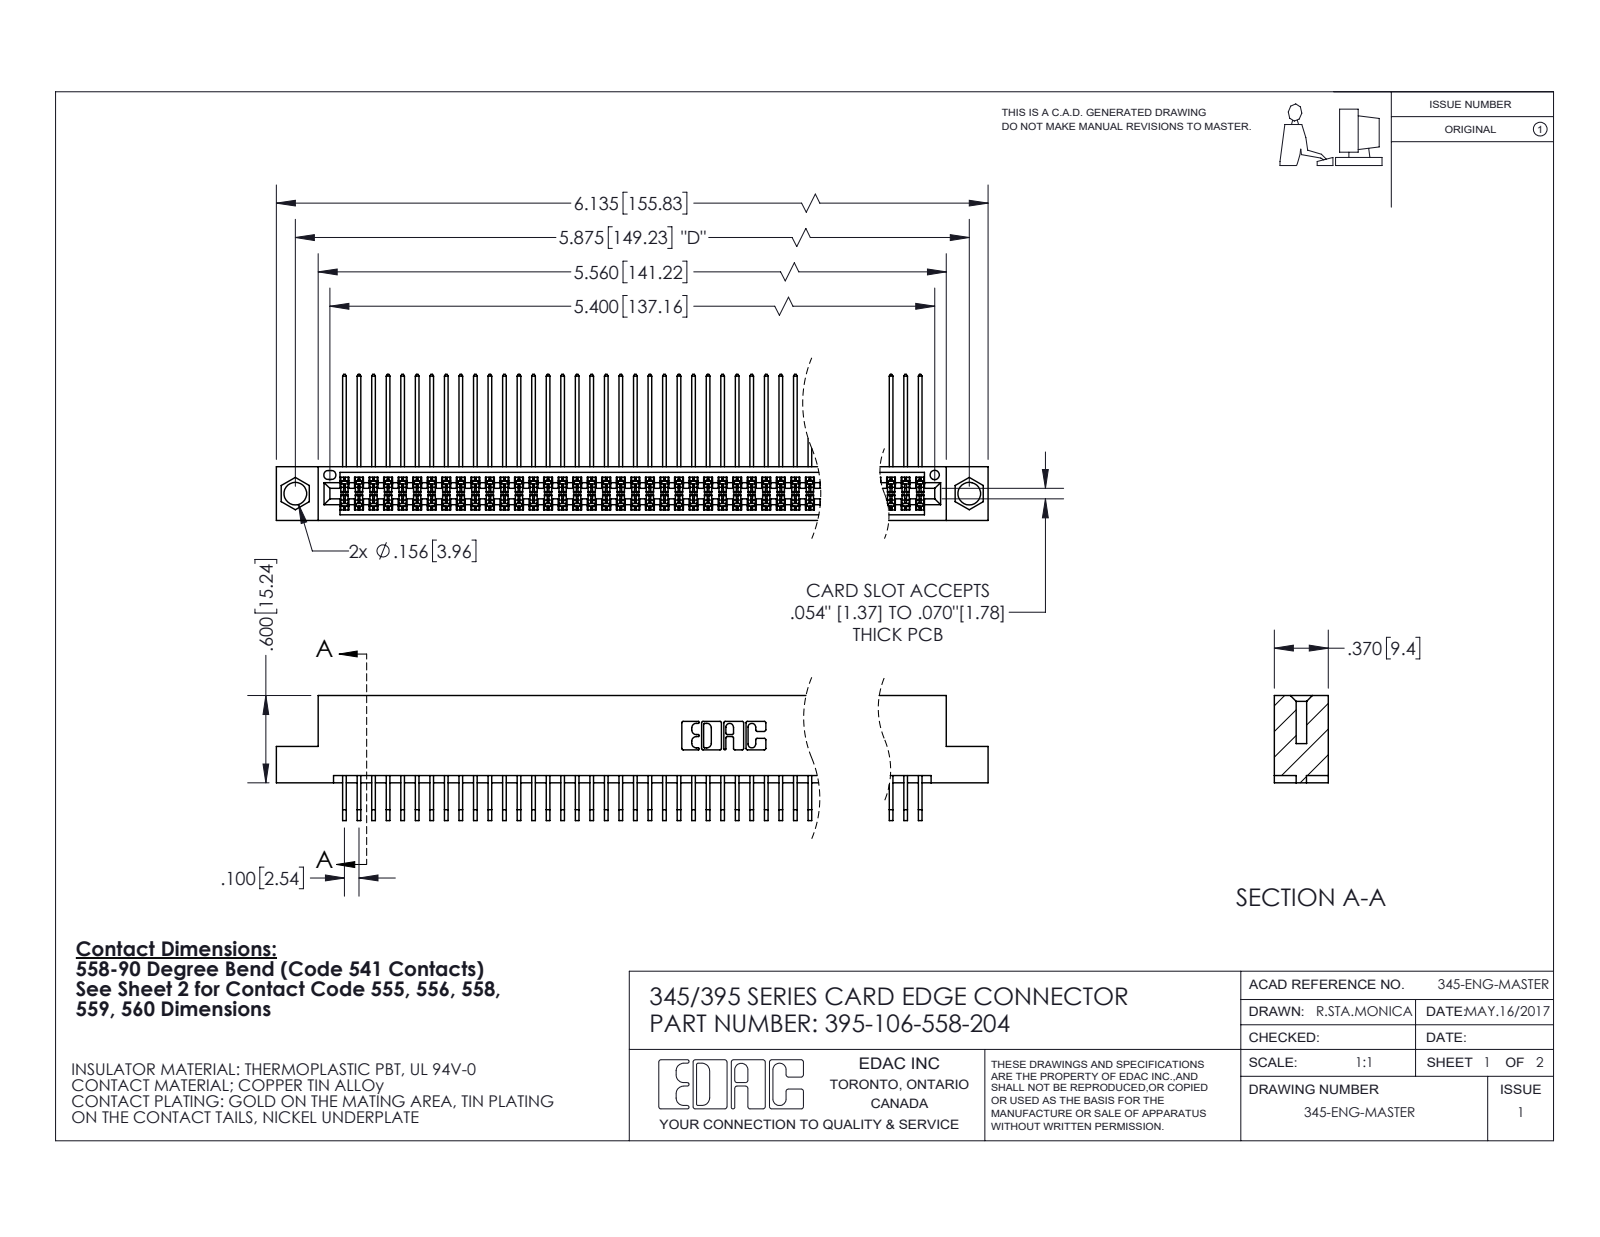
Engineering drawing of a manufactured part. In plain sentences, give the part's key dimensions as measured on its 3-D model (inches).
The part is named "345 Part_Flush Mounting Lugs - 0.156 Dia-TI; 345-292-001_558 559 Tail - 1; 345-292-001_558 Tail - 2; 395-106-558-204". Its 3-D file was written by "SolidWorks 2020 (CONFIG_CONTROL_DESIGN)". It is 107 solids with 5652 faces: 3804 planar, 1848 cylindrical and 0 other. Overall it measures 6.135 by 1.005 by 0.859 inches. Its volume is 0.961 cubic inches and its surface area 40.63 square inches. Round holes: 2 of diameter 0.156, 1 of diameter 0.064. Partial cylindrical surfaces (rounded edges, fillets, slot ends): 212 of radius 0.006, 22 of radius 0.01, 6 of radius 0.007, 6 of radius 0.031, 3 of radius 0.026, 2 of radius 0.014, 2 of radius 0.019, 2 of radius 0.022. The main face-to-face distances are 0.072, 0.298, 0.2, 0.37, 0.098, 0.272, 0.025, 0.225, 0.025, 0.175. The hole center spacings are 0.27, 5.639, 5.875.
